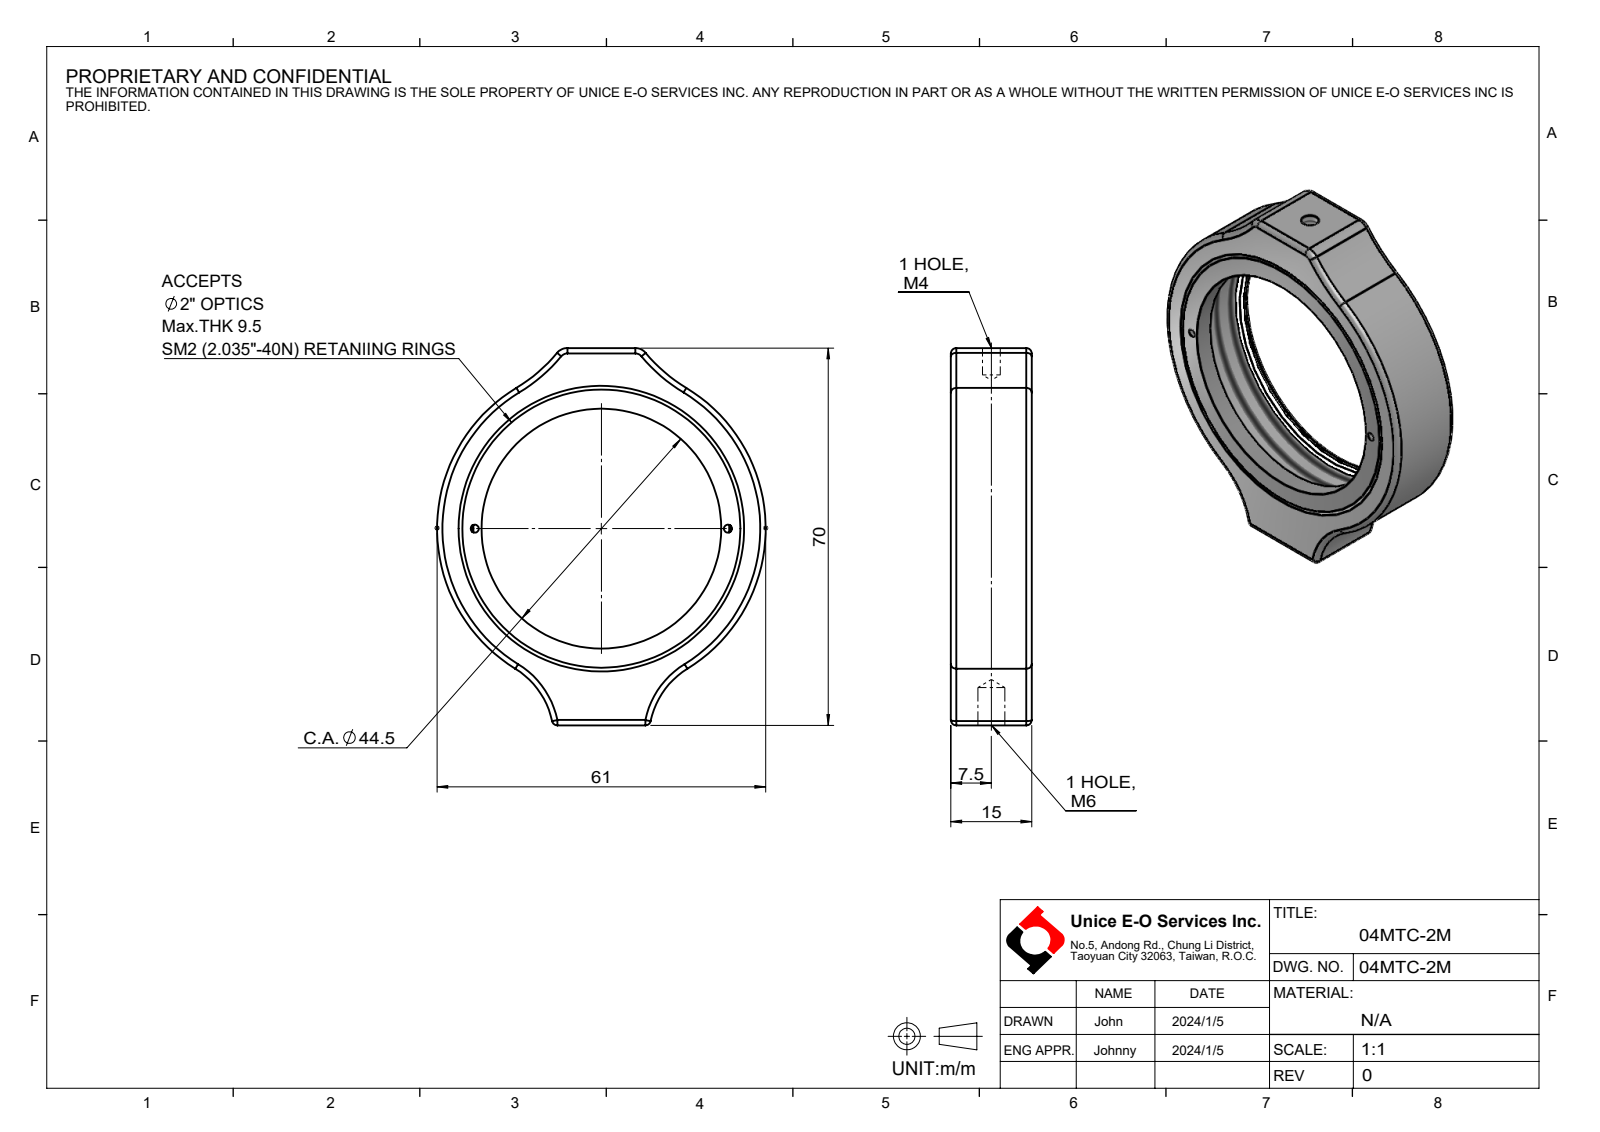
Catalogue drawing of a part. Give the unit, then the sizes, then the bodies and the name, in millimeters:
Units: millimetres
Overall size (bounding box): 70 × 61 × 15
Round holes (diameter × count): ⌀1.5 ×2, ⌀3.3 ×1, ⌀5 ×1, ⌀44.5 ×1, ⌀47.5 ×1, ⌀48 ×1, ⌀51 ×1
Round bosses / shafts (diameter × count): ⌀51.6 ×1, ⌀50 ×1
Partial cylindrical surfaces — rounded edges, fillets, slot ends (radius × count): R1 ×6, R2.5 ×2, R15 ×2, R30 ×2, R30.5 ×1
Main face-to-face distances: 15, 1, 11.5, 3.5, 10.5, 14, 70, 2, 9.5, 13
Hole centre spacings: 23.5, 47
Volume: 18 280 mm³ · Surface area: 10 811 mm²
Bodies: 3 solids, 78 faces (9 planar, 35 cylindrical, 34 other)
Part name (STEP PRODUCT): 04MTC-2M
STEP written by: SolidWorks 2016 (CONFIG_CONTROL_DESIGN)
